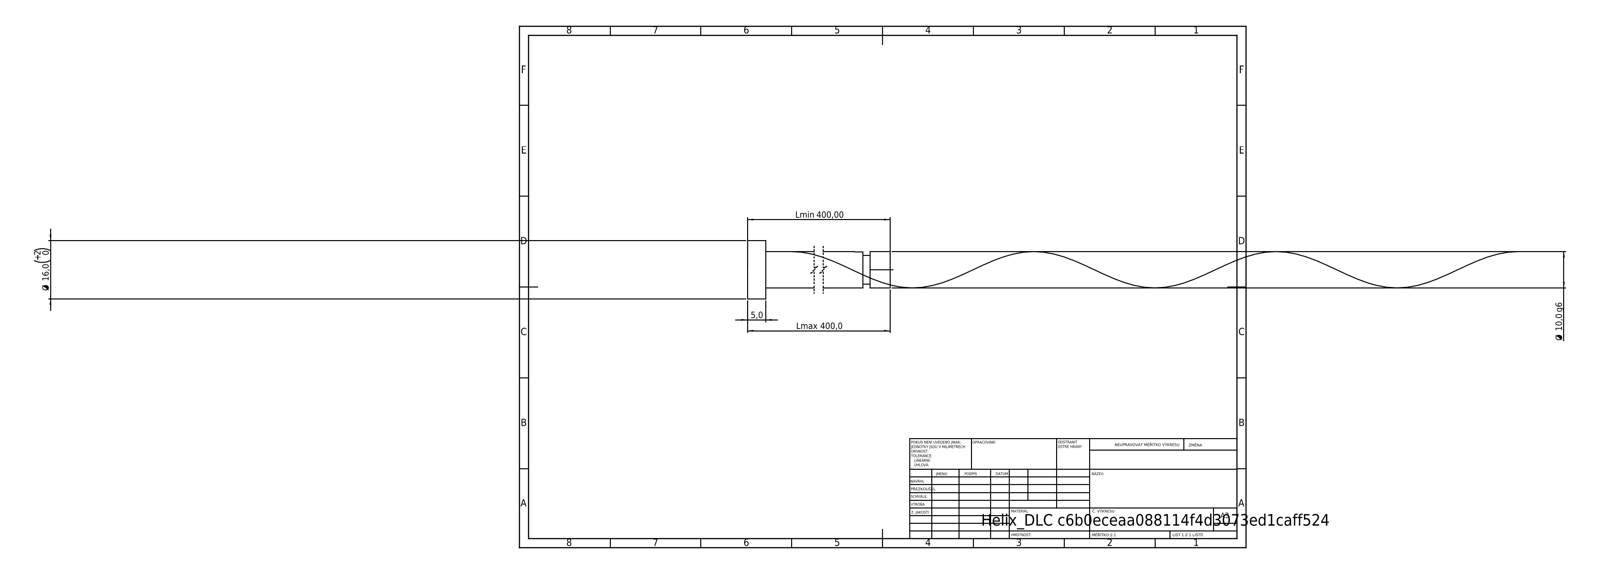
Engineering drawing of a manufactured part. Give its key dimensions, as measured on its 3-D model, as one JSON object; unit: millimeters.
{"step_written_by": "SolidWorks 2019 (CONFIG_CONTROL_DESIGN)", "units": "millimeters", "bodies": {"solids": 1, "faces": 21, "planar": 6, "cylindrical": 14, "other": 1}, "overall_size": [400, 16, 16], "volume_mm3": 31671, "surface_area_mm2": 13324, "round_bosses_or_shafts": [[16, 1], [10, 1], [8, 1]], "face_to_face_distances": [5, 400, 395, 394.47, 389.47, 5.53, 392.47, 387.47, 2, 7.53]}
